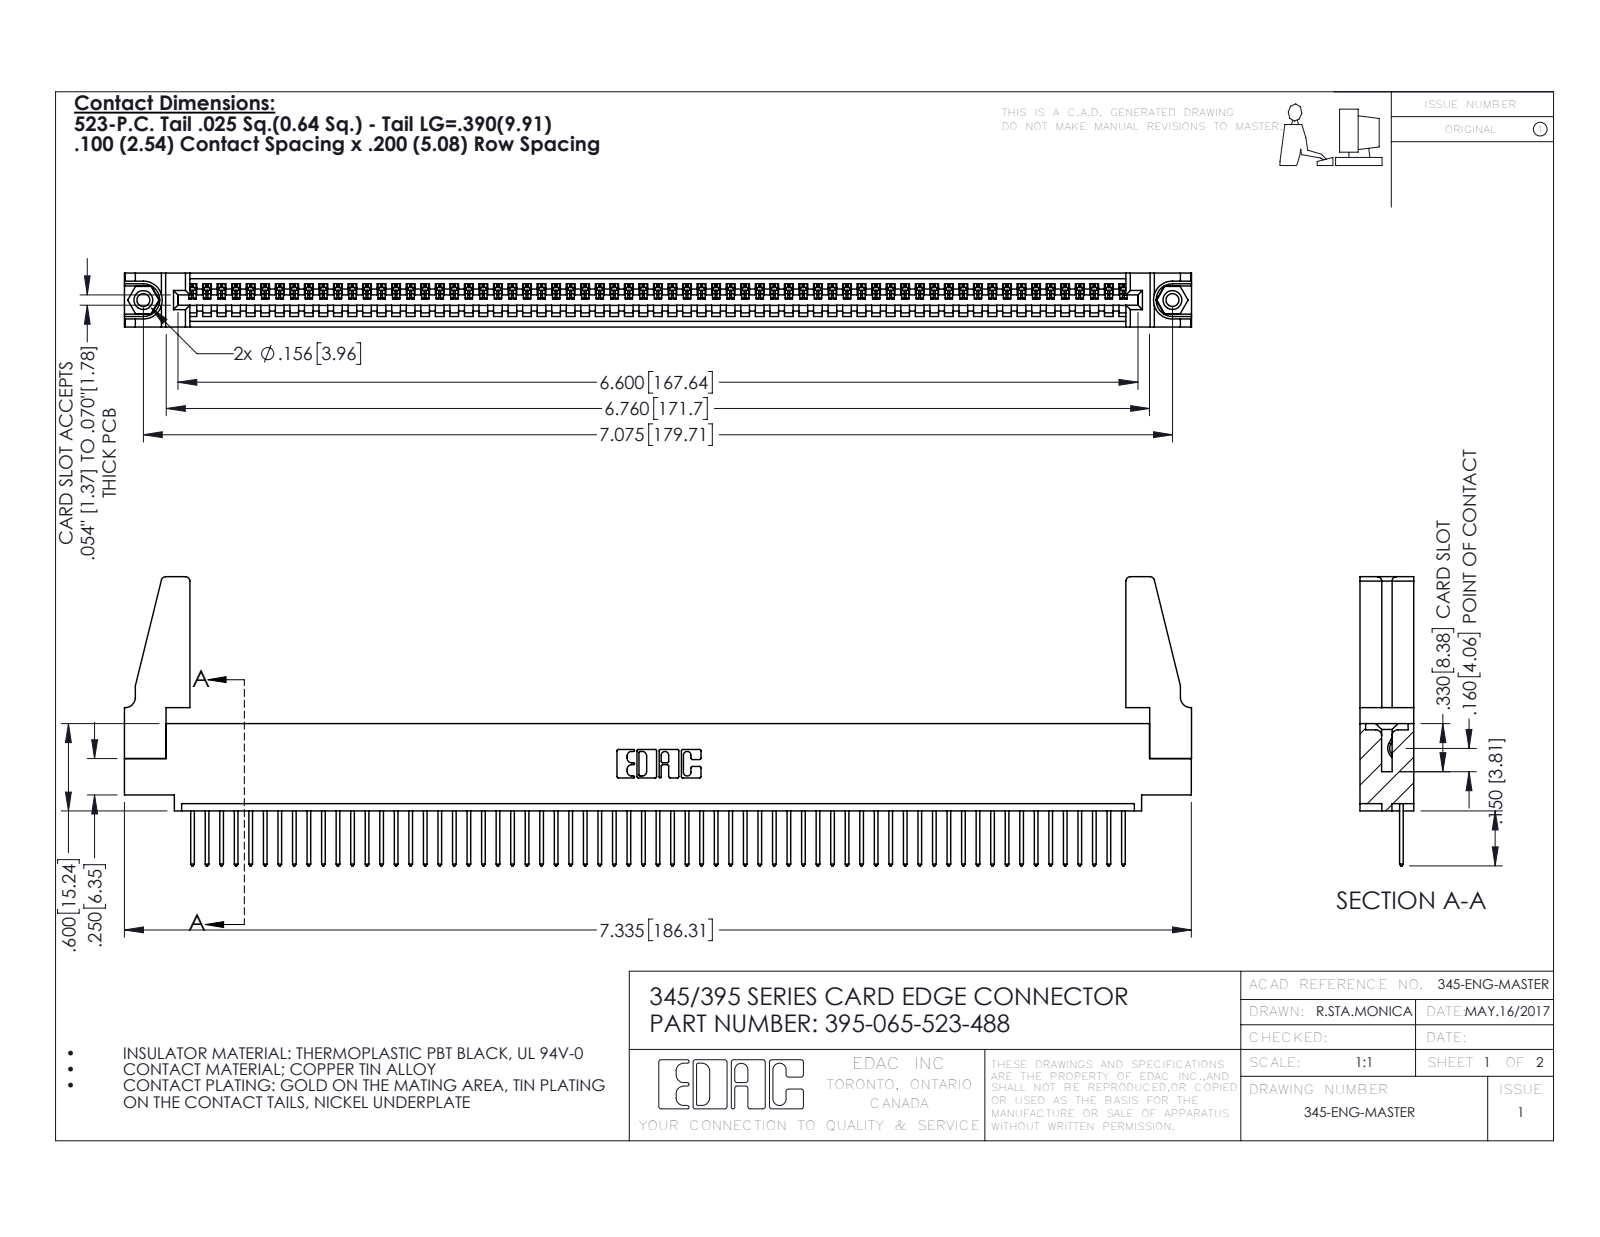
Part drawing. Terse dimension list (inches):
name: 345-250-001_345-250-001-102; 395-065-523-488; 345-292-001_345-293-123; 345 Part_0.110 Offset - 0.156 Dia-TH (+1 more)
written by: SolidWorks 2016 (CONFIG_CONTROL_DESIGN)
unit: in
bodies: 70 solids, 4024 faces (2756 planar, 1252 cylindrical, 16 other)
size: 7.336 × 1.987 × 0.37
volume: 1.284 in³; area: 42.21 in²
holes: 2× ⌀0.089, 2× ⌀0.125, 2× ⌀0.156, 1× ⌀0.064
bosses: 2× ⌀0.155
rounds: 130× R0.006, 130× R0.01, 22× R0.01, 8× R0.03, 6× R0.007, 6× R0.031, 3× R0.026, 2× R0.031
face distances: 0.072, 0.298, 0.37, 0.098, 0.272, 0.025, 0.2, 0.225, 0.149, 0.072
hole spacings: 0.27, 6.839, 7.075
